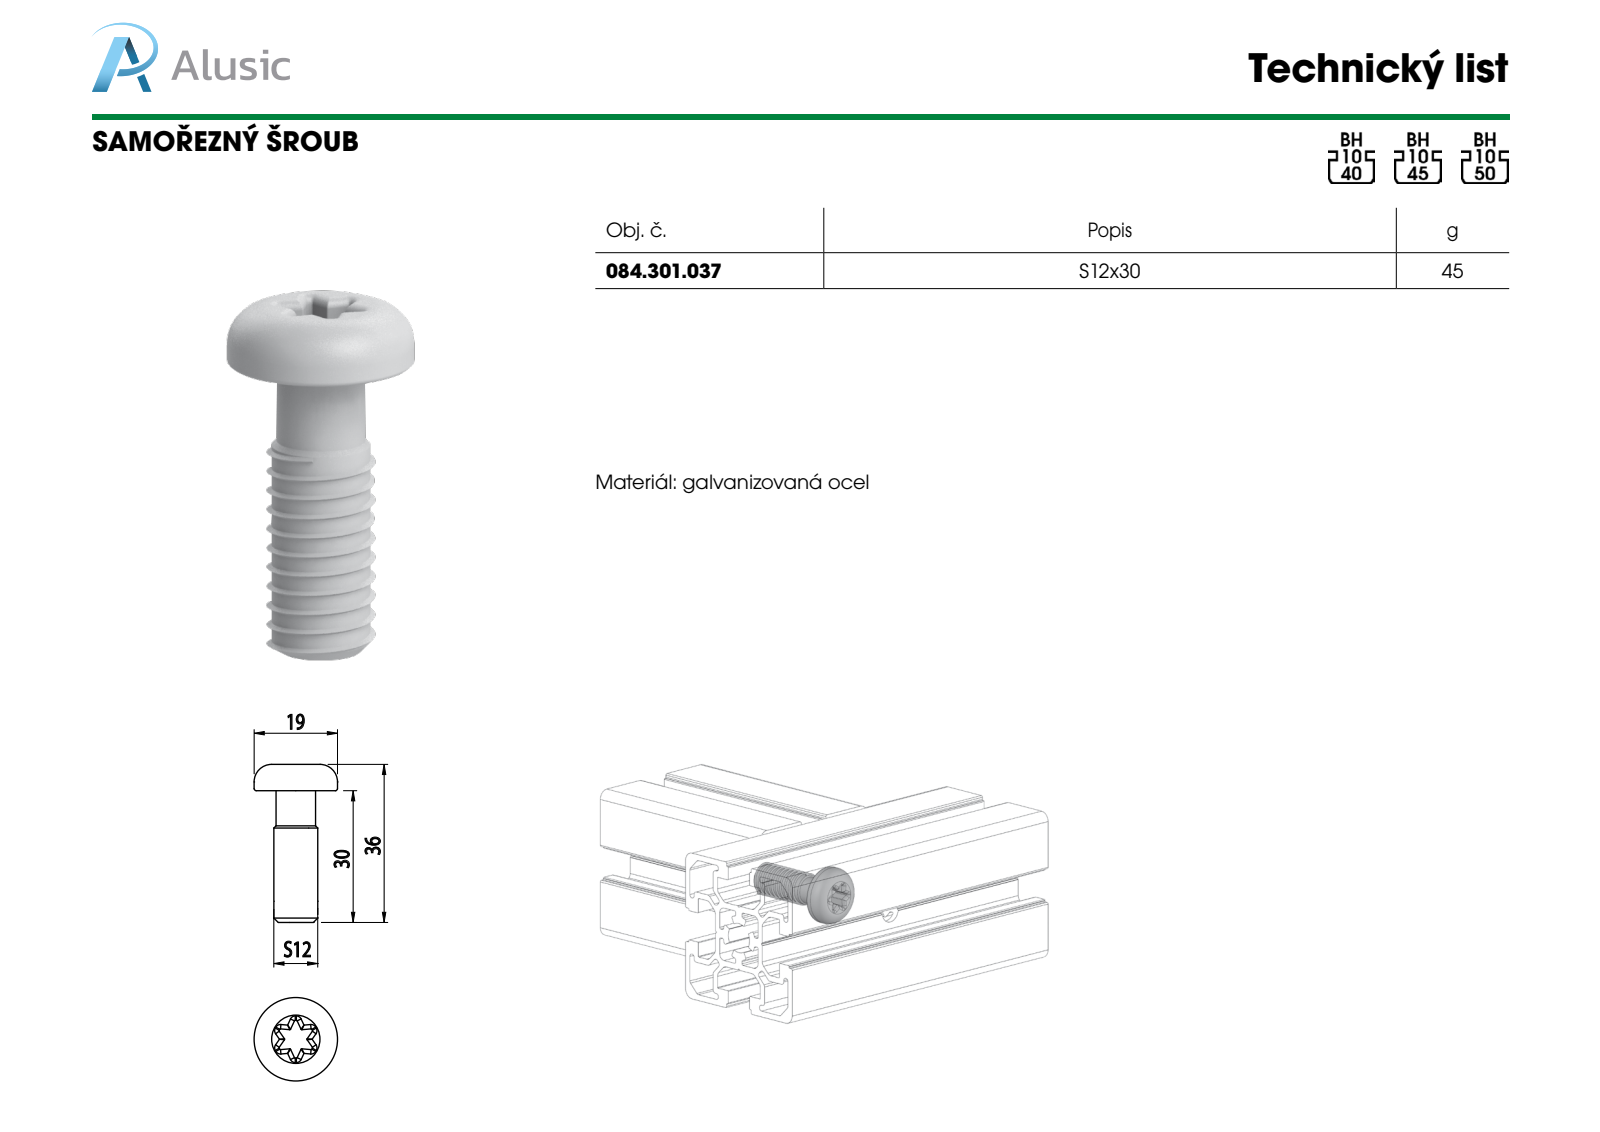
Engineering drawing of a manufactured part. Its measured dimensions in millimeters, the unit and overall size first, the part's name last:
Units: millimetres
Overall size (bounding box): 36 × 19 × 19
Round bosses / shafts (diameter × count): ⌀19 ×1, ⌀10 ×1, ⌀9 ×1
Partial cylindrical surfaces — rounded edges, fillets, slot ends (radius × count): R0.2 ×18, R1 ×18
Main face-to-face distances: 4.1, 30, 36, 6, 8.62
Volume: 3 571 mm³ · Surface area: 2 125 mm²
Bodies: 1 solid, 122 faces (24 planar, 67 cylindrical, 31 other)
Part name (STEP PRODUCT): 084.301.037
STEP written by: SolidWorks 2011 (CONFIG_CONTROL_DESIGN)
